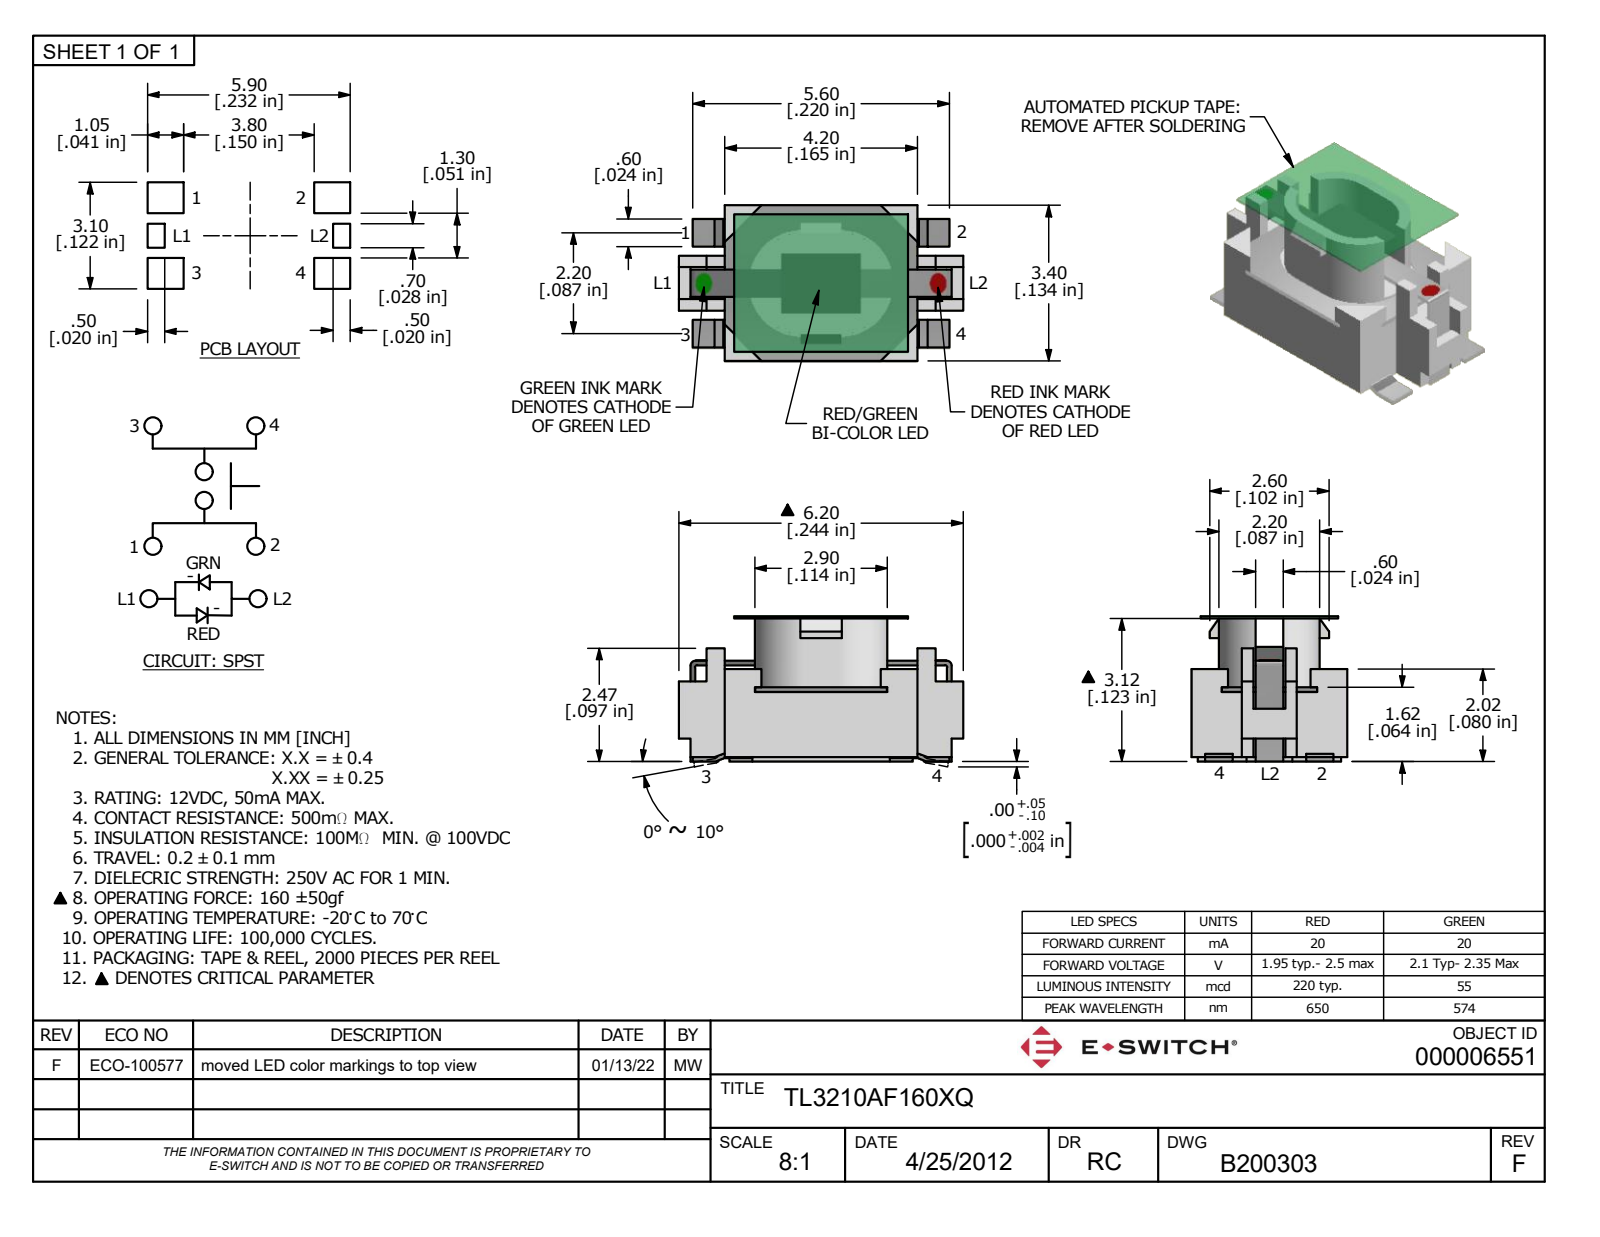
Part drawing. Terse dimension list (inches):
name: P:\\E-Switch Secure\\3D_MODELS_STP_FORMAT\\TL3210AF160xQ.stp
written by: ACIS (CONFIG_CONTROL_DESIGN)
unit: in
bodies: 1 solid, 208 faces (192 planar, 16 cylindrical, 0 other)
size: 0.244 × 0.134 × 0.123
volume: 0.002 in³; area: 0.23 in²
rounds: 2× R0.004, 2× R0.033, 2× R0.043, 2× R0.045, 2× R0.053
face distances: 0.02, 0.043, 0.024, 0.064, 0.035, 0.026, 0.016, 0.037, 0.018, 0.079
